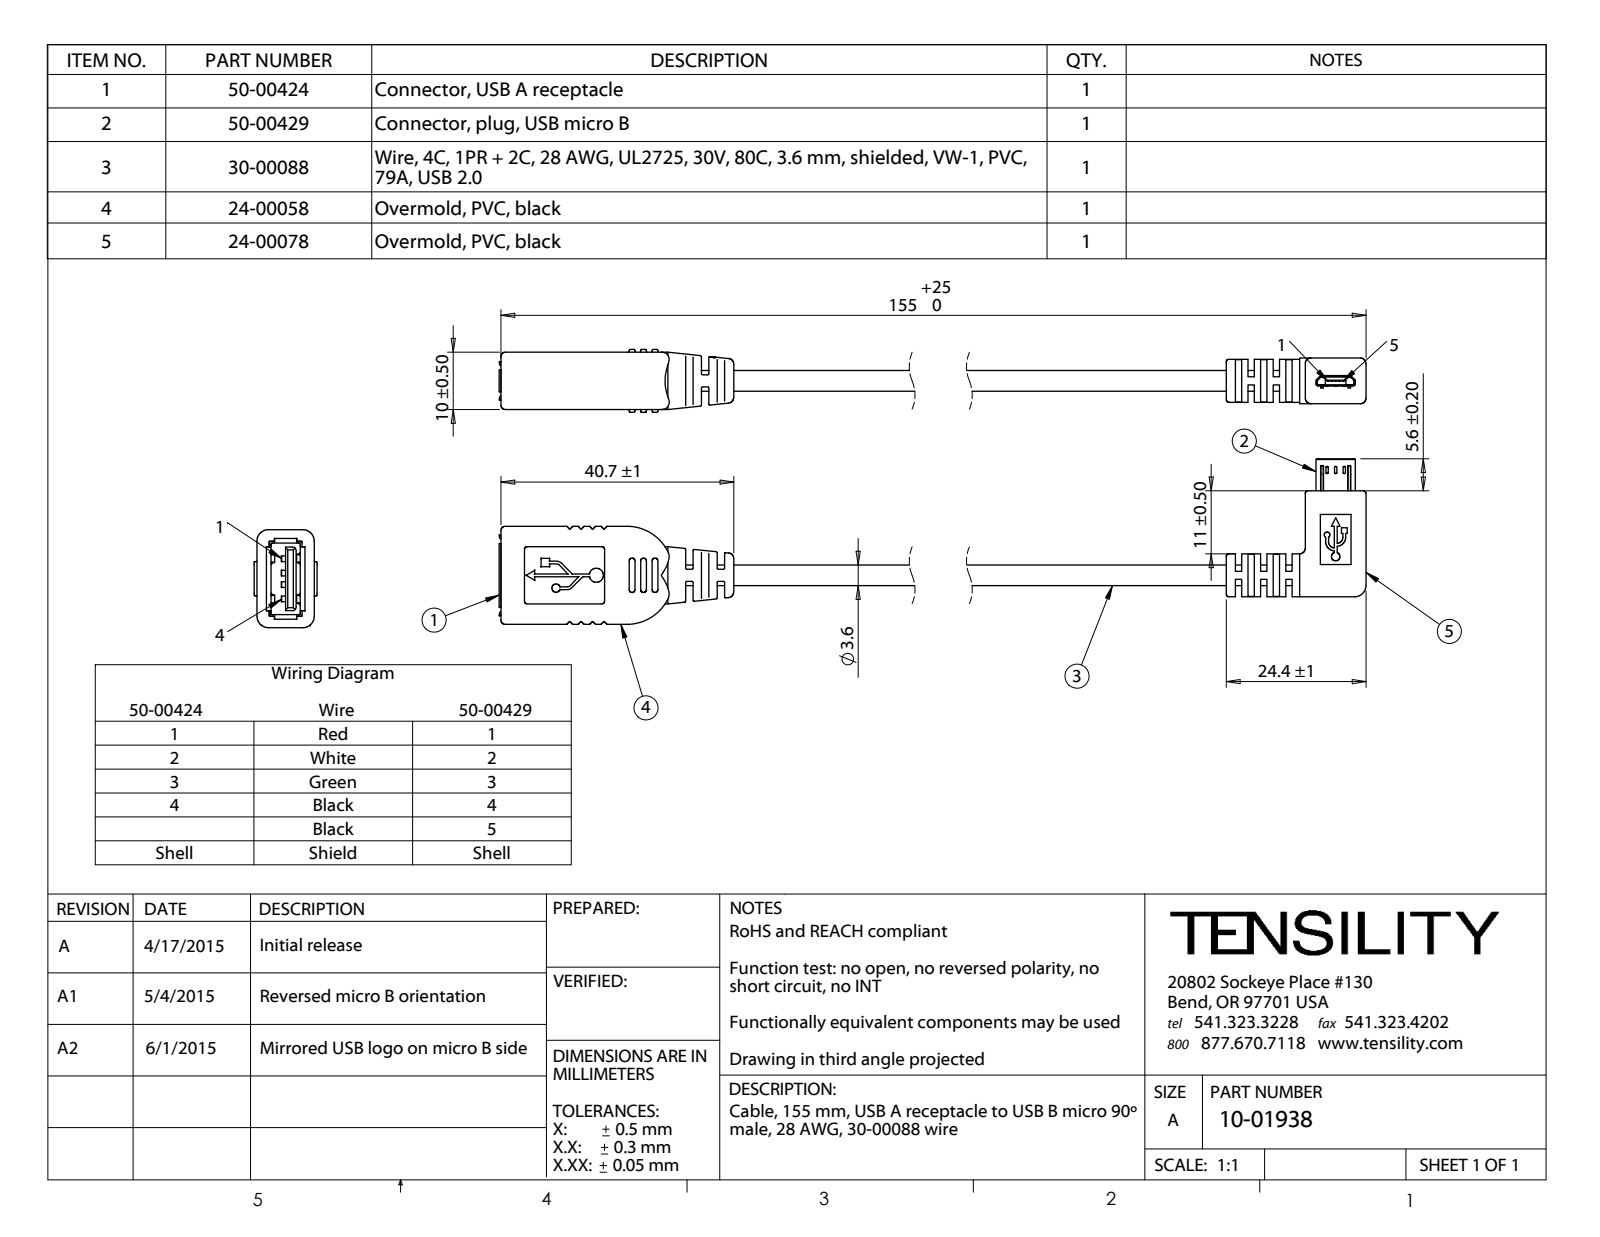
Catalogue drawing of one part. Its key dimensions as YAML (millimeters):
part_name: "30-00088_blunt cut; 50-00424 shell; 50-00424; 24-00058_connector cutout (+6 more)"
step_written_by: "SolidWorks 2015 (CONFIG_CONTROL_DESIGN)"
units: millimeters
bodies: {solids: 107, faces: 1466, planar: 617, cylindrical: 541, other: 308}
overall_size: [195.46, 28.9, 11]
volume: 8300
surface_area: 19096
round_holes:
  - {diameter: 2.52, count: 1}
round_bosses_or_shafts:
  - {diameter: 0.85, count: 4}
  - {diameter: 7.5, count: 1}
  - {diameter: 4.55, count: 1}
  - {diameter: 3.6, count: 1}
  - {diameter: 3.51, count: 1}
  - {diameter: 3.11, count: 1}
  - {diameter: 2.45, count: 1}
  - {diameter: 1.5, count: 1}
partial_cylinders:
  - {radius: 0.2, count: 37}
  - {radius: 0.5, count: 18}
  - {radius: 0.1, count: 15}
  - {radius: 1, count: 11}
  - {radius: 0.4, count: 10}
  - {radius: 0.13, count: 8}
  - {radius: 2, count: 7}
  - {radius: 0.32, count: 4}
face_to_face_distances: [0.31, 2.44, 7.56, 2.19, 1.1, 4.4, 2.2, 7.31, 10, 1]
hole_center_spacings: [0.84, 0.91, 0.74, 0.87, 0.78, 0.97, 1.23, 0.86]
